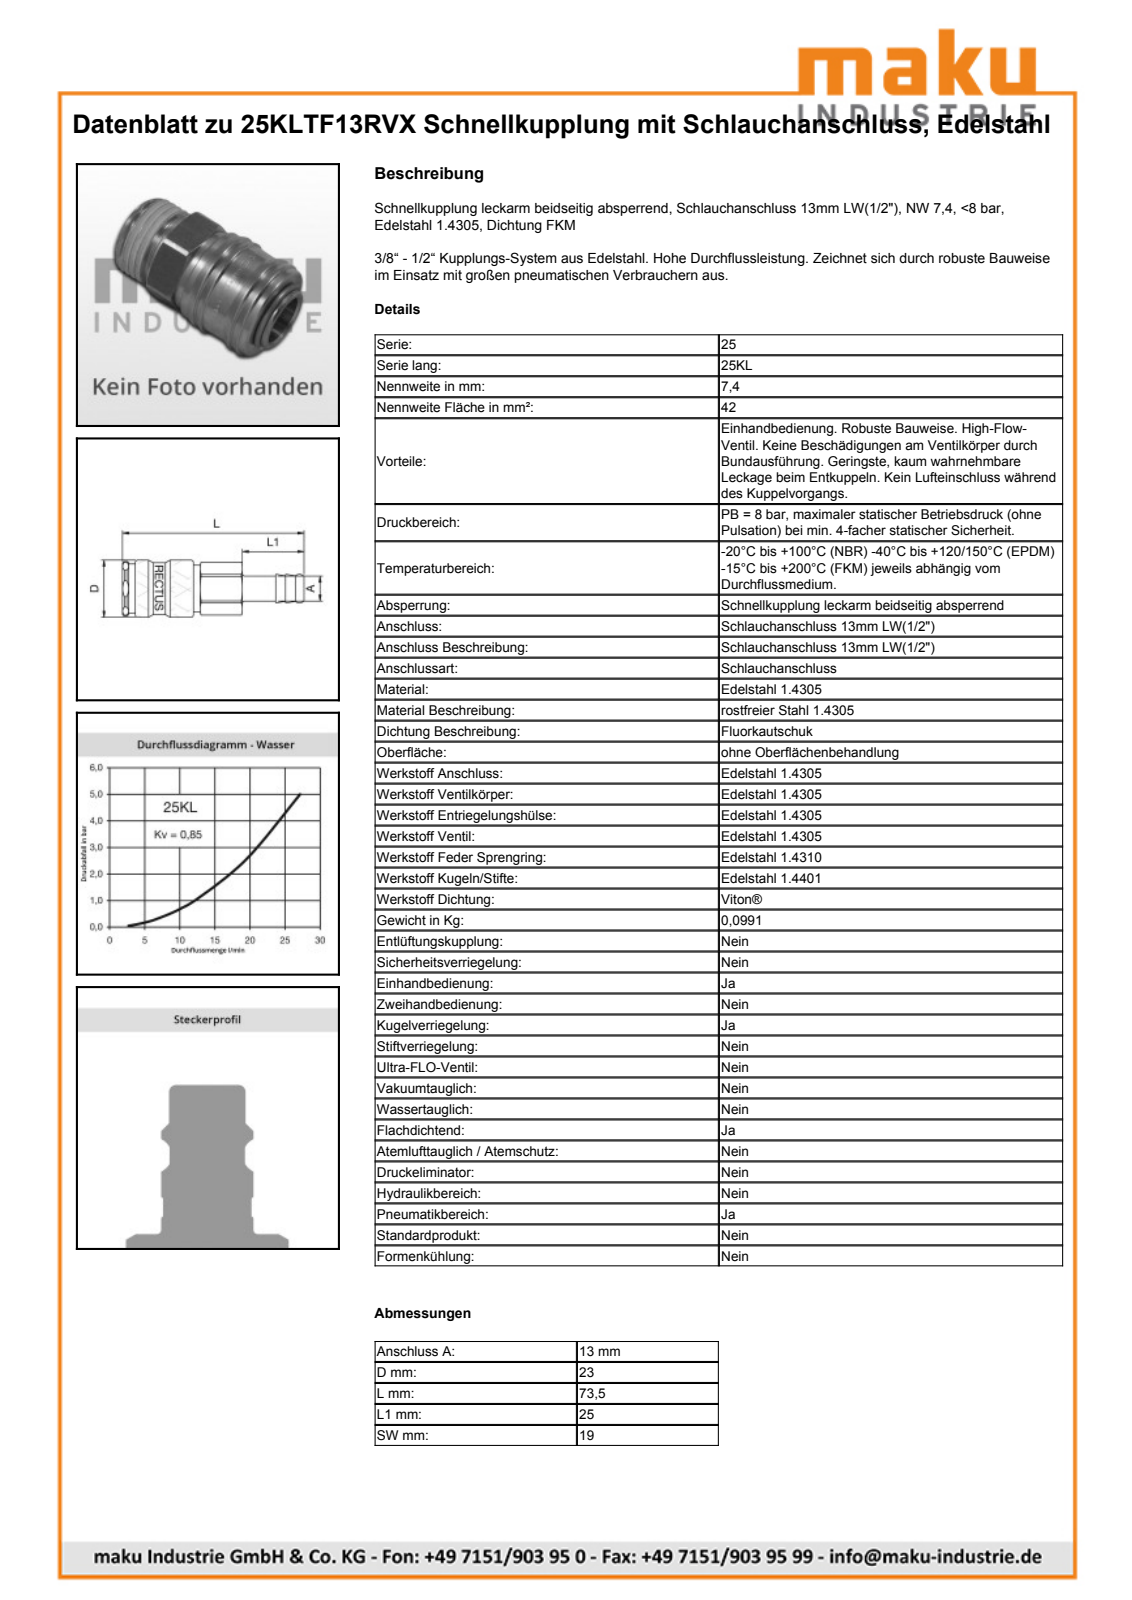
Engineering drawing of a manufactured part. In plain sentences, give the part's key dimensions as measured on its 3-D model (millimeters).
The part is named "D105795". Its 3-D file was written by "Autodesk Inventor 2011 (AUTOMOTIVE_DESIGN)". It is 2 solids with 605 faces: 210 planar, 79 cylindrical and 316 other. Overall it measures 73.5 by 23.15 by 23.15 millimeters. Its volume is 19 423 cubic millimeters and its surface area 8 225 square millimeters. Round holes: 1 of diameter 17.25, 1 of diameter 19.35, 1 of diameter 20.05. Round bosses or shafts: 1 of diameter 23.15, 1 of diameter 21, 1 of diameter 20, 1 of diameter 18.95, 1 of diameter 16, 1 of diameter 13.1. Partial cylindrical surfaces (rounded edges, fillets, slot ends): 1 of radius 7.01, 1 of radius 10.4, 1 of radius 10.7, 1 of radius 11. The main face-to-face distances are 19, 73.5, 48.5, 25, 24.5, 24, 49, 28.69, 4.19, 19.81.
